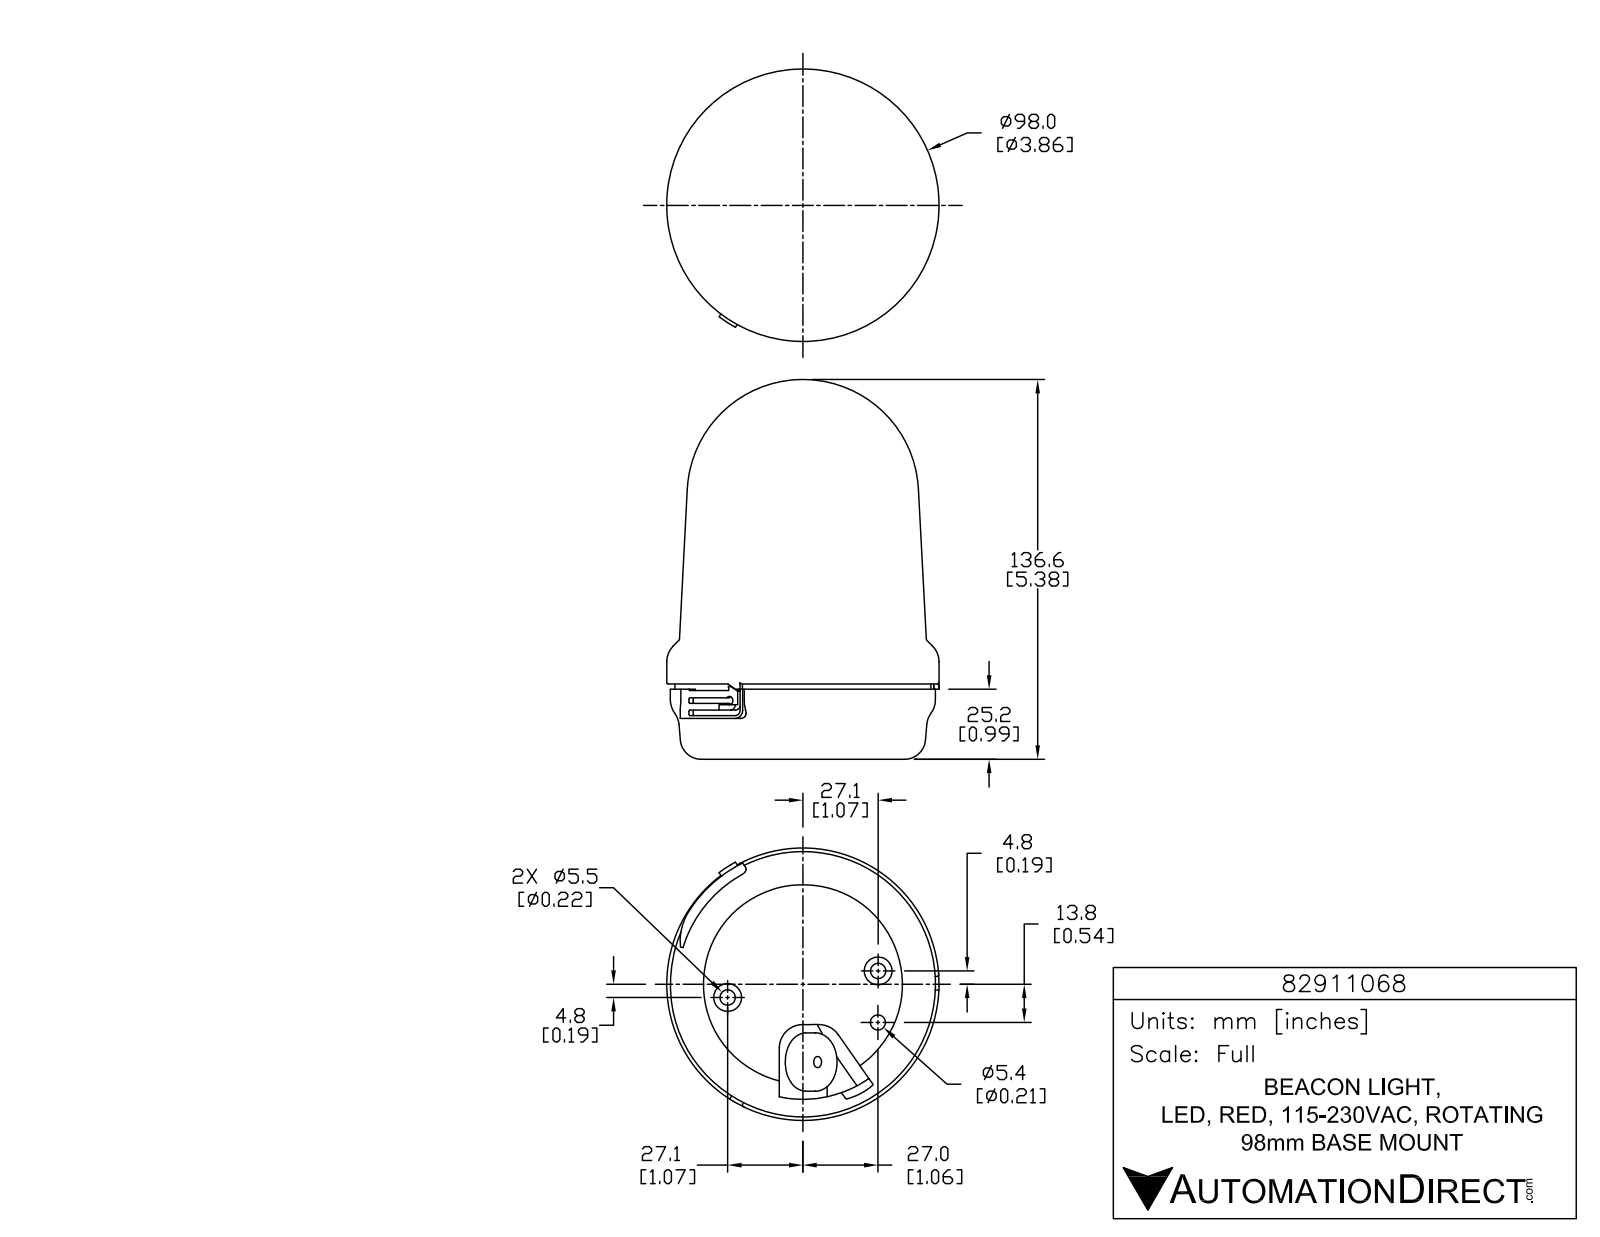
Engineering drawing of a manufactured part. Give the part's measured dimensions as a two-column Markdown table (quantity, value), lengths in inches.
| quantity | value |
| --- | --- |
| part name | 82911068 |
| STEP written by | SolidWorks 2015 (AUTOMOTIVE_DESIGN) |
| units | inches |
| bodies | 1 solid, 872 faces (566 planar, 204 cylindrical, 102 other) |
| overall size | 5.378 × 3.858 × 3.858 |
| volume | 44.69 in³ |
| surface area | 73.66 in² |
| round holes (diameter × count) | 0.059 × 3, 0.217 × 2, 0.157 × 1, 0.213 × 1, 2.819 × 1 |
| round bosses / shafts (diameter × count) | 0.339 × 3, 0.084 × 3, 0.394 × 2, 3.858 × 1, 3.756 × 1, 3.626 × 1, 0.827 × 1 |
| partial cylindrical surfaces (radius × count) | 0.005 × 9, 0.005 × 6, 0.012 × 6, 0.012 × 6, 0.012 × 6, 0.196 × 6, 0.02 × 5, 0.039 × 4 |
| main face-to-face distances | 1.045, 0.972, 0.073, 0.02, 0.992, 1.065, 0.236, 0.579, 0.559, 0.413 |
| hole center spacings | 1.083, 0.73, 1.193, 2.158, 2.165 |
